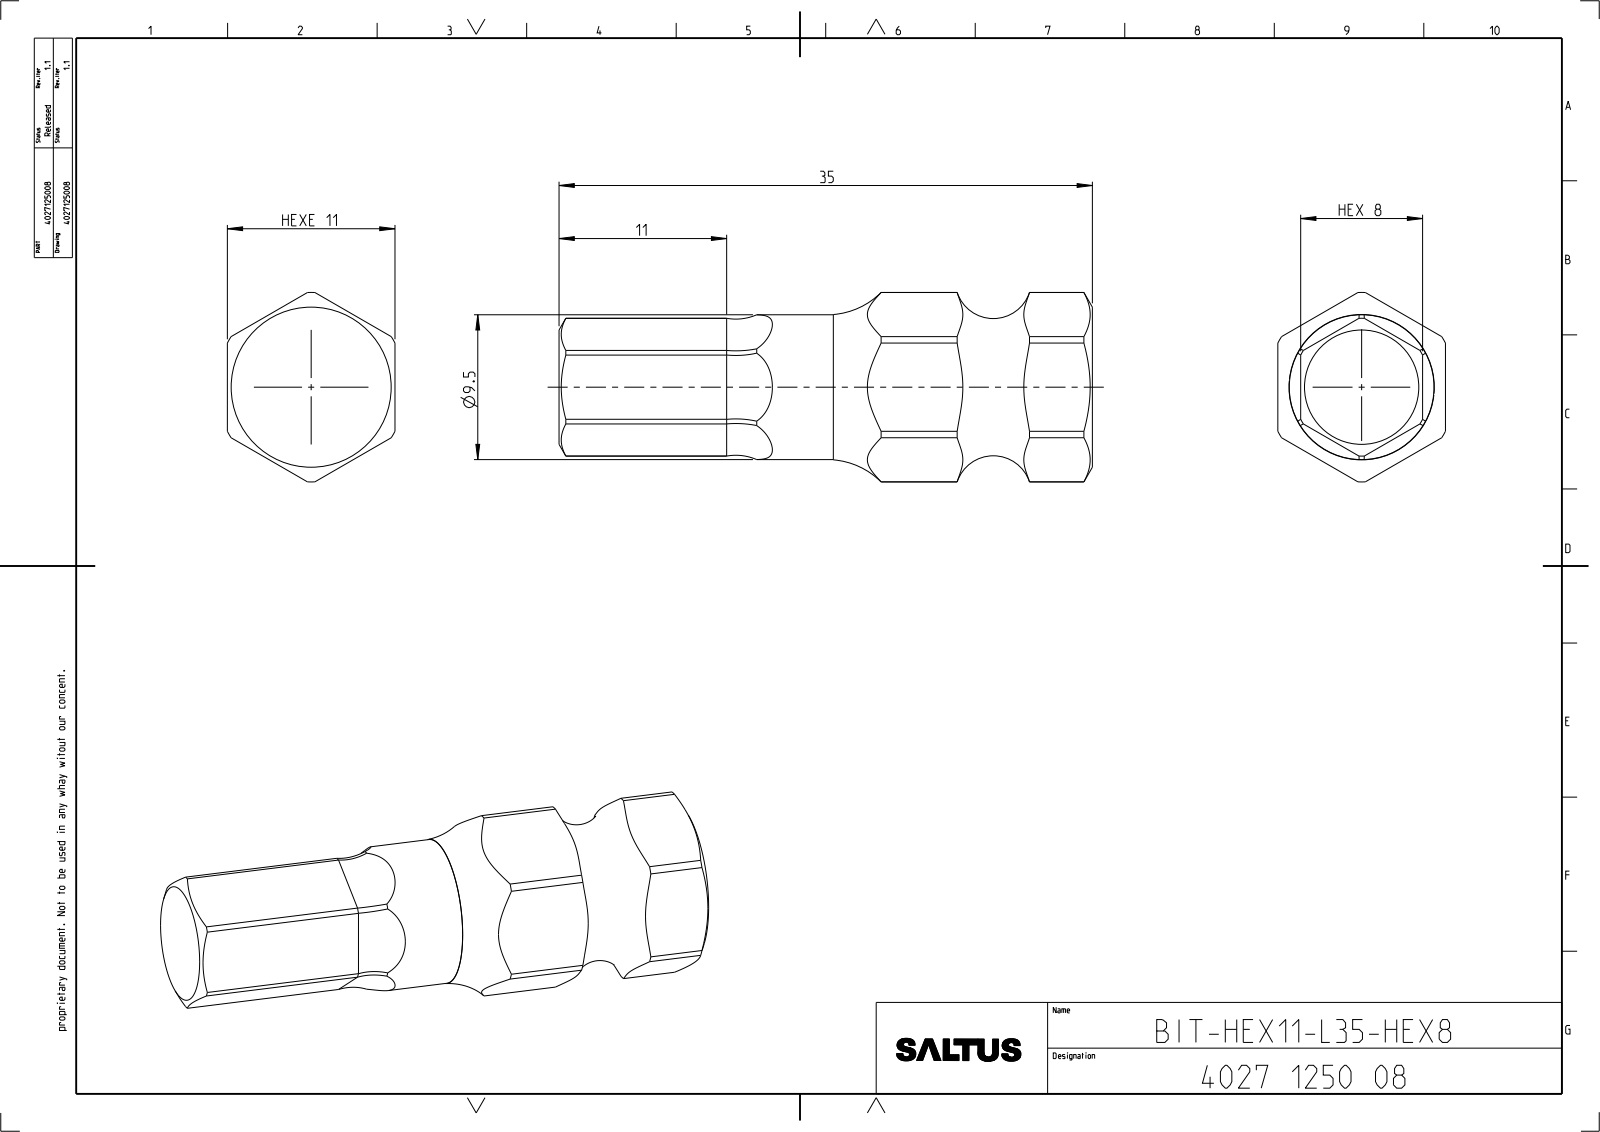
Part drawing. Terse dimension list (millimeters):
name: 4027125008
written by: CREO PARAMETRIC BY PTC INC, 2022414 (CONFIG_CONTROL_DESIGN)
unit: mm
bodies: 1 solid, 61 faces (21 planar, 26 cylindrical, 14 other)
size: 35 × 12.43 × 11
volume: 2 654 mm³; area: 1 288 mm²
bosses: 1× ⌀9.5
rounds: 6× R4, 1× R4.52, 1× R6.21
face distances: 1.5, 9.5, 11, 8, 35, 17, 18
